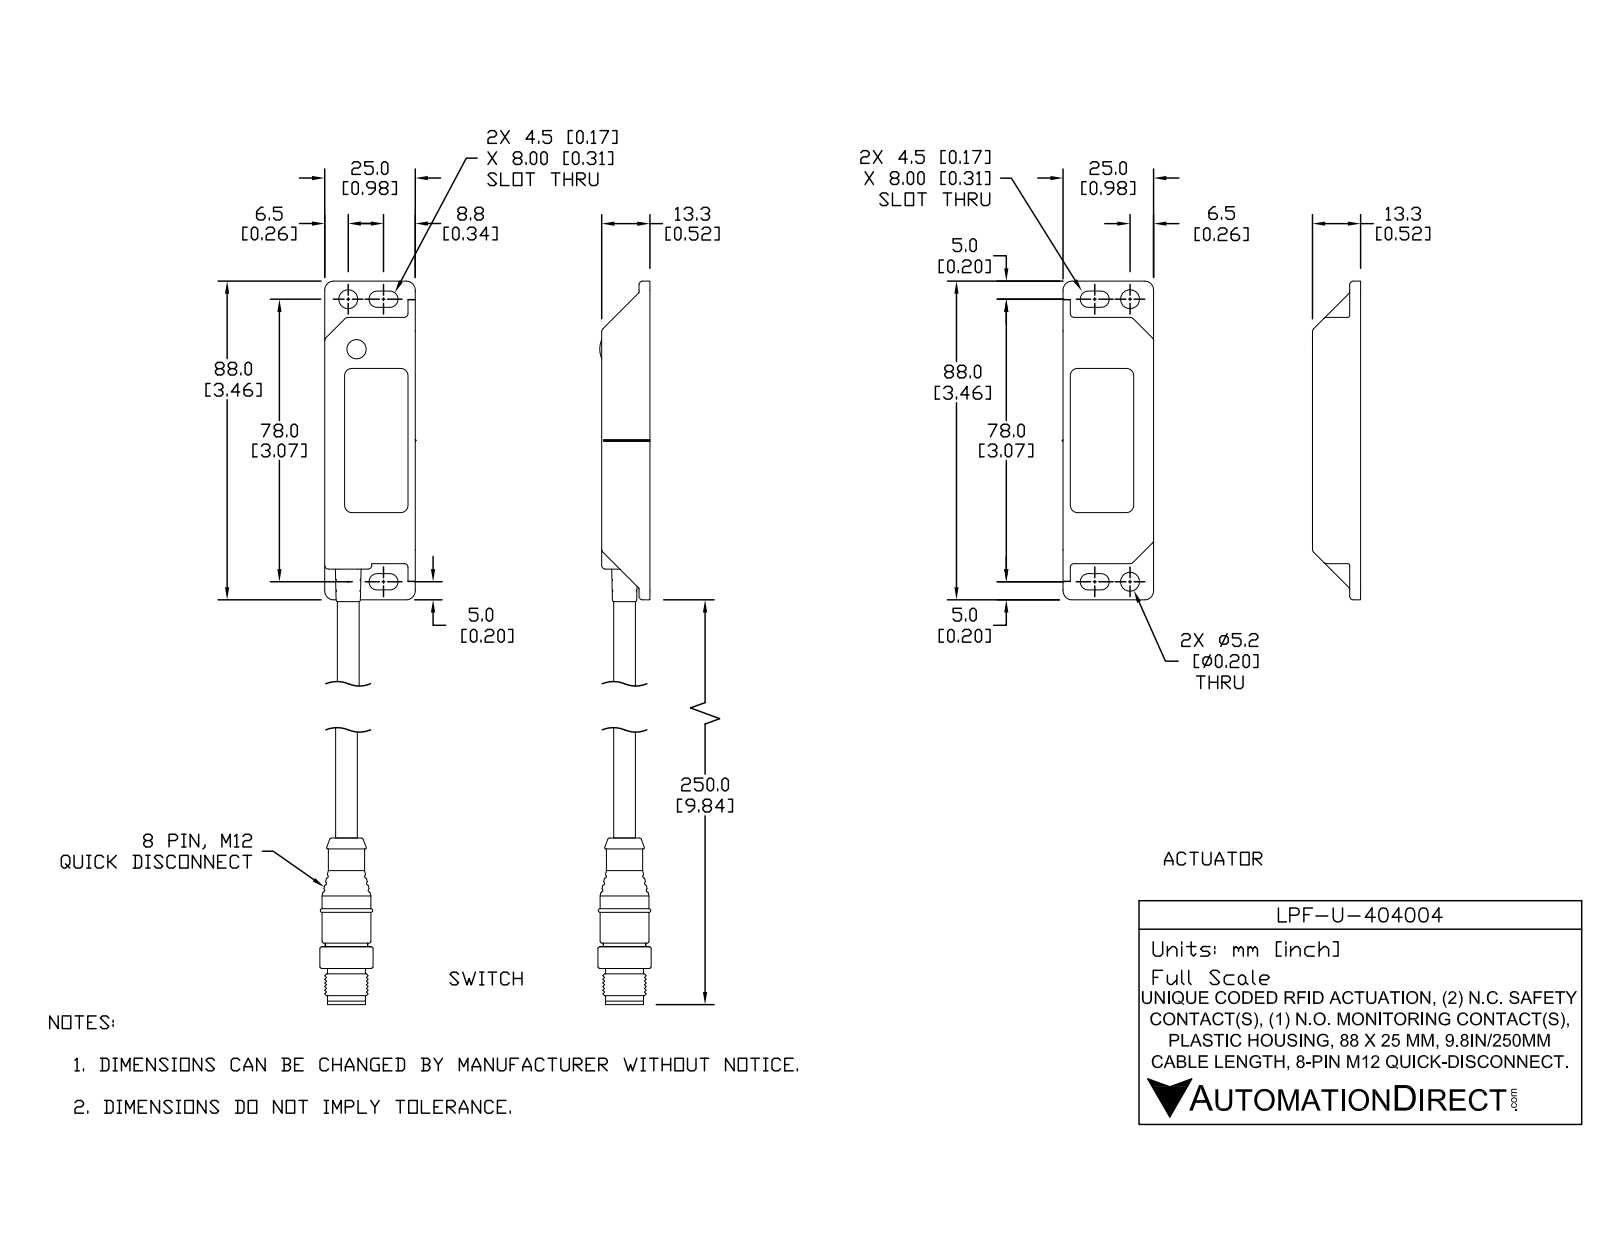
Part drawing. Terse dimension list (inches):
name: LPF-U-404004; LPF-U-404004_2; LPF-U-404004_1
written by: SolidWorks 2017 (AUTOMOTIVE_DESIGN)
unit: in
bodies: 12 solids, 1419 faces (558 planar, 417 cylindrical, 444 other)
size: 12.972 × 2.026 × 0.579
volume: 2.034 in³; area: 54.51 in²
holes: 4× ⌀0.197, 4× ⌀0.205, 1× ⌀0.119, 1× ⌀0.173, 1× ⌀0.213, 1× ⌀0.232, 1× ⌀0.276, 1× ⌀0.327, 1× ⌀0.465
bosses: 8× ⌀0.031, 4× ⌀0.079, 2× ⌀0.193, 2× ⌀0.091, 1× ⌀0.531, 1× ⌀0.461, 1× ⌀0.413, 1× ⌀0.394
rounds: 116× R0.02, 49× R0.039, 10× R0.079, 8× R0.089, 8× R0.098, 6× R0.012, 1× R0.189, 1× R0.289
face distances: 0.067, 0.441, 0.079, 0.374, 0.059, 0.071, 0.508, 0.445, 0.512, 0.988
hole spacings: 0.748, 1.097, 1.19, 1.275, 1.48, 1.571, 1.784, 1.895
